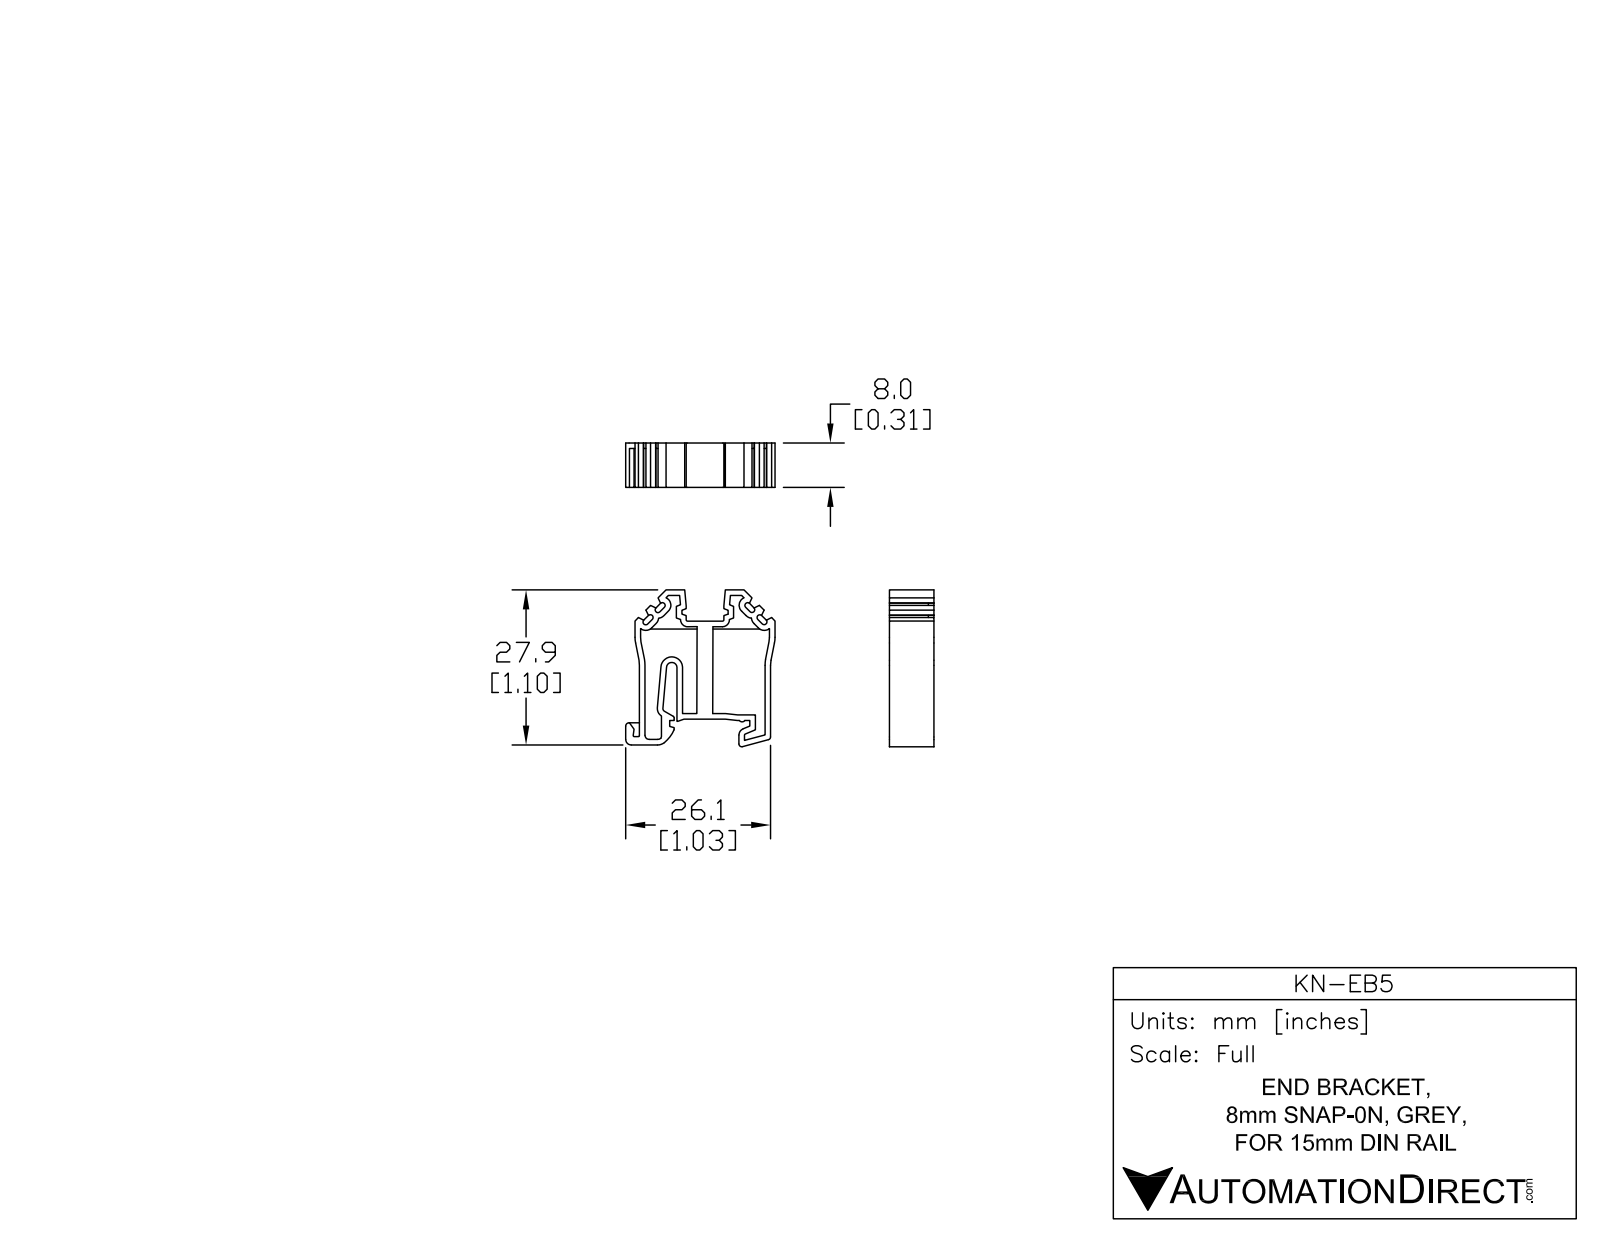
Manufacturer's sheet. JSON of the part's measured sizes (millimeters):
{"part_name": "KN-EB5", "step_written_by": "SolidWorks 2014 (AUTOMOTIVE_DESIGN)", "units": "millimeters", "bodies": {"solids": 1, "faces": 262, "planar": 181, "cylindrical": 80, "other": 1}, "overall_size": [28.21, 26.87, 8], "volume_mm3": 2556, "surface_area_mm2": 3348, "partial_cylinders_radius": [[0.5, 8], [1.5, 8], [5, 4], [0.2, 3], [0.5, 3], [0.25, 2], [1.25, 2], [4, 2]], "face_to_face_distances": [2.37, 5.63, 1, 3.26, 8, 22.6, 6.76, 15.84, 23.6, 1.73]}
